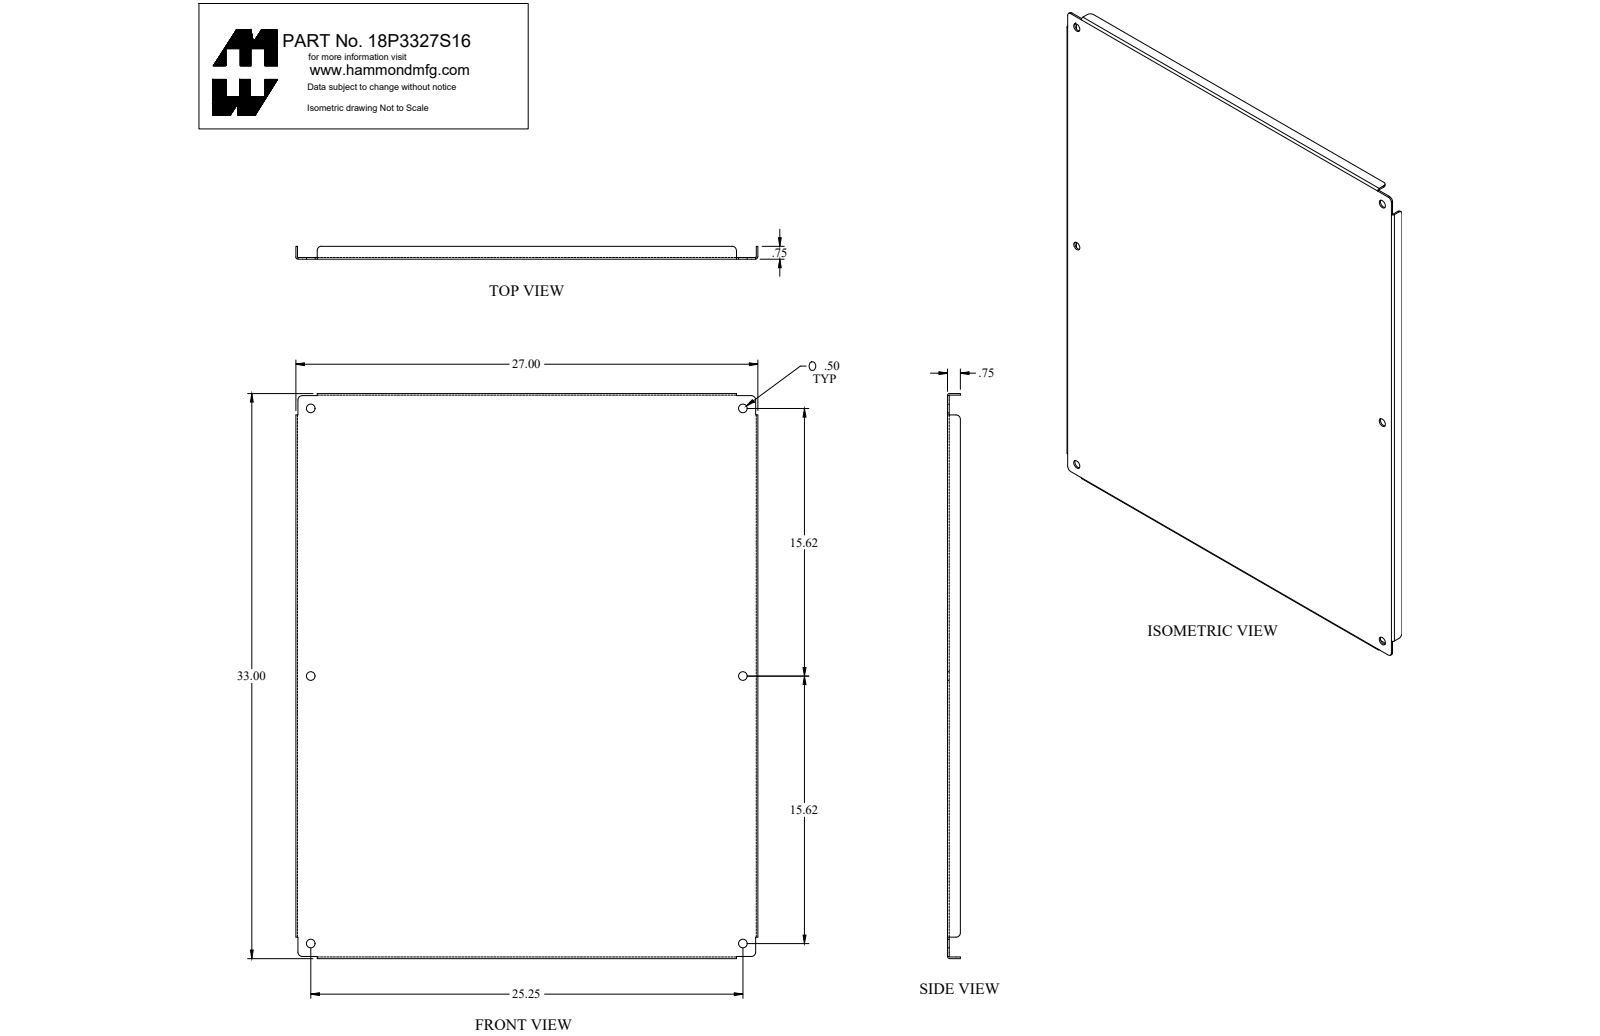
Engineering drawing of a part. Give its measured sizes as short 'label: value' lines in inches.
name: 18P3327S16_Default
written by: SolidWorks 2018 (CONFIG_CONTROL_DESIGN)
unit: in
bodies: 1 solid, 62 faces (30 planar, 32 cylindrical, 0 other)
size: 33 × 27 × 0.75
volume: 90.9 in³; area: 1 926 in²
holes: 6× ⌀0.5
rounds: 8× R0.25, 4× R0.03, 4× R0.125
face distances: 0.095, 26.905, 32.905, 27, 26.81, 33, 32.81, 0.75, 0.655, 0.125
hole spacings: 15.625, 29.694, 25.25, 31.25, 40.177
